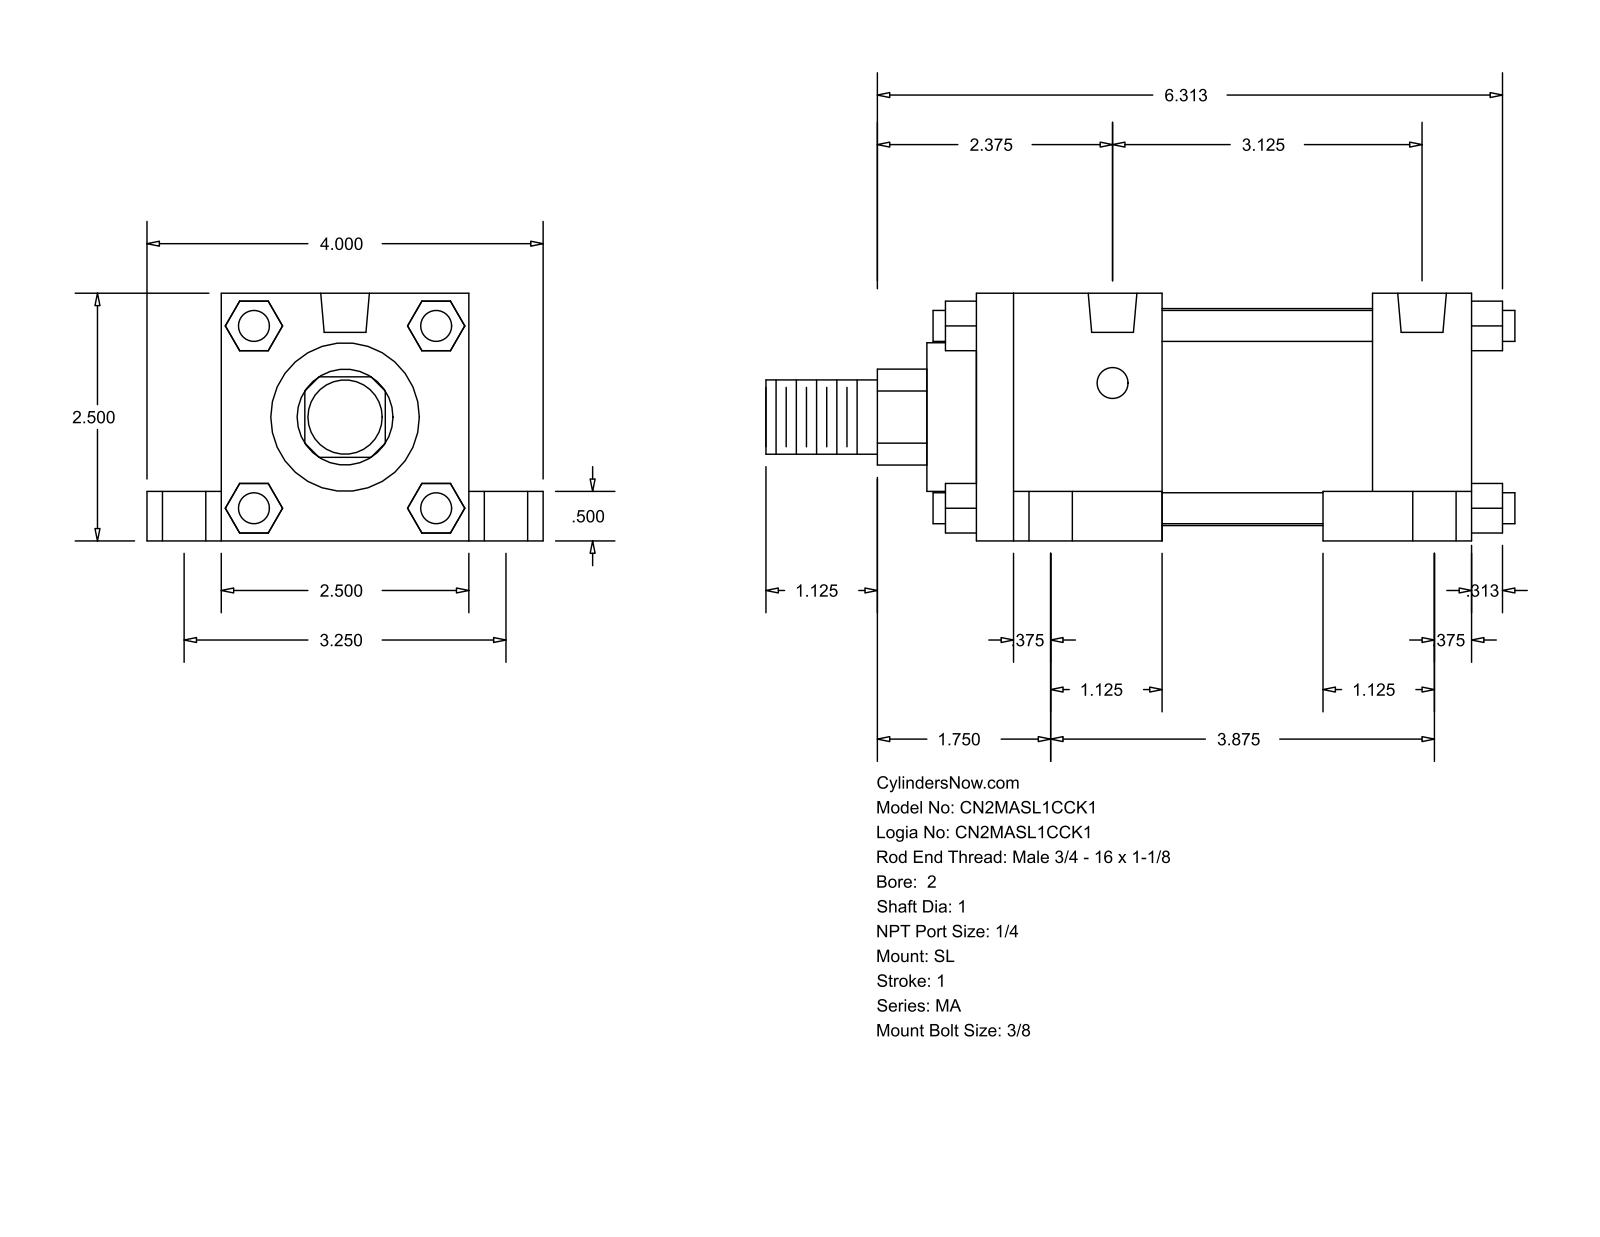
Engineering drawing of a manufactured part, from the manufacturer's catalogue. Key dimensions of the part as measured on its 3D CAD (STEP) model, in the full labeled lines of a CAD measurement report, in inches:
Part name (STEP PRODUCT): MA_SL__0200_1
STEP written by: GSSL Pune (CONFIG_CONTROL_DESIGN)
Units: inches
Bodies: 0 solids, 148 faces (112 planar, 36 cylindrical, 0 other)
Overall size (bounding box): 7.563 × 4 × 2.5
Round holes (diameter × count): ⌀0.313 ×4, ⌀0.437 ×4, ⌀0.687 ×4, ⌀0.492 ×2
Round bosses / shafts (diameter × count): ⌀0.313 ×4, ⌀2.19 ×1, ⌀1.5 ×1, ⌀1 ×1, ⌀0.75 ×1
Partial cylindrical surfaces — rounded edges, fillets, slot ends (radius × count): R0.484 ×1
Main face-to-face distances: 2.5, 0.5, 4, 5, 2.125, 0.75, 3.25, 1, 2, 1.875
Hole centre spacings: 1.63, 1.741, 3.125, 3.25, 3.633, 3.875, 4.087, 5.057
